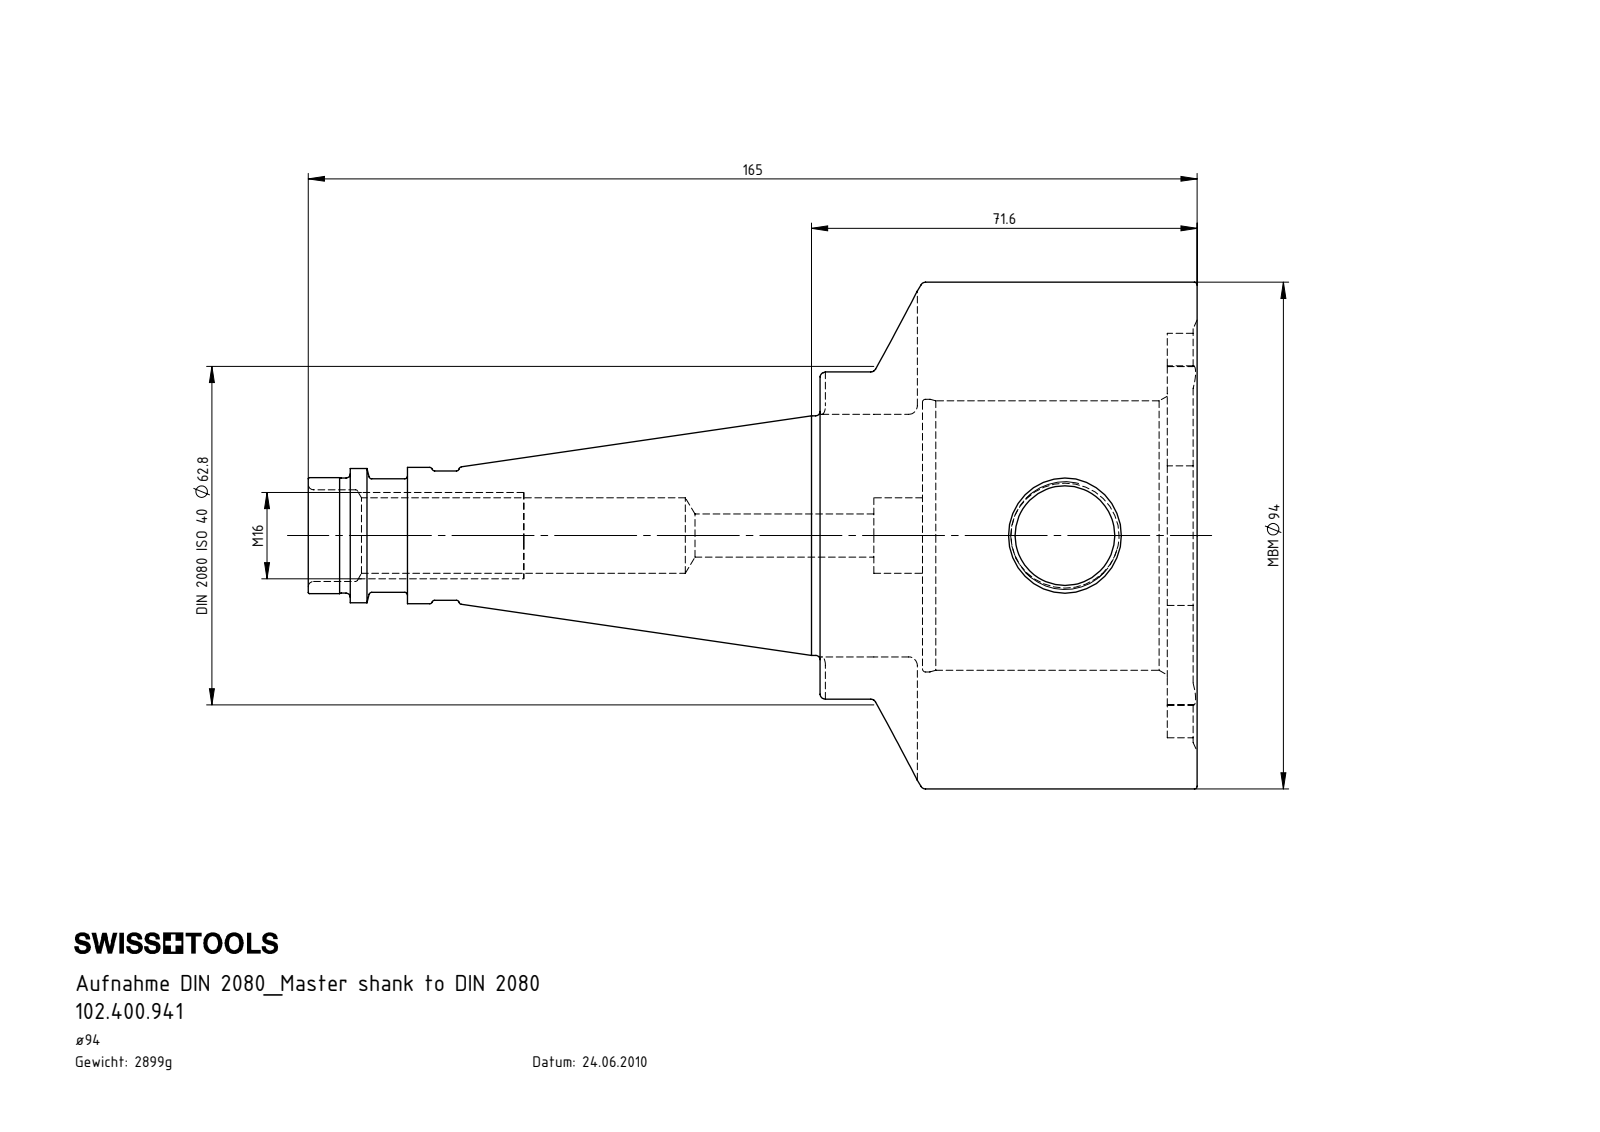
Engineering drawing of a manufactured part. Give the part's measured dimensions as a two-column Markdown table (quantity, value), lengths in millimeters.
| quantity | value |
| --- | --- |
| part name | 102.400.941 |
| STEP written by | SolidWorks 2017 (CONFIG_CONTROL_DESIGN) |
| units | millimeters |
| bodies | 1 solid, 139 faces (28 planar, 53 cylindrical, 58 other) |
| overall size | 165 × 94 × 94 |
| volume | 369 751 mm³ |
| surface area | 53 579 mm² |
| round holes (diameter × count) | 8.5 × 1, 14 × 1, 17 × 1, 18.5 × 1, 50 × 1, 50.6 × 1 |
| round bosses / shafts (diameter × count) | 94 × 1, 62.8 × 1, 44.45 × 1, 25.3 × 1, 24.91 × 1, 24 × 1, 21.5 × 1, 21.35 × 1 |
| partial cylindrical surfaces (radius × count) | 1.6 × 8, 5.2 × 4, 8.05 × 1, 30 × 1, 37.52 × 1 |
| main face-to-face distances | 45.45, 51, 5.55, 19, 64.45, 70, 69.25, 50.25, 4.8, 0.75 |
